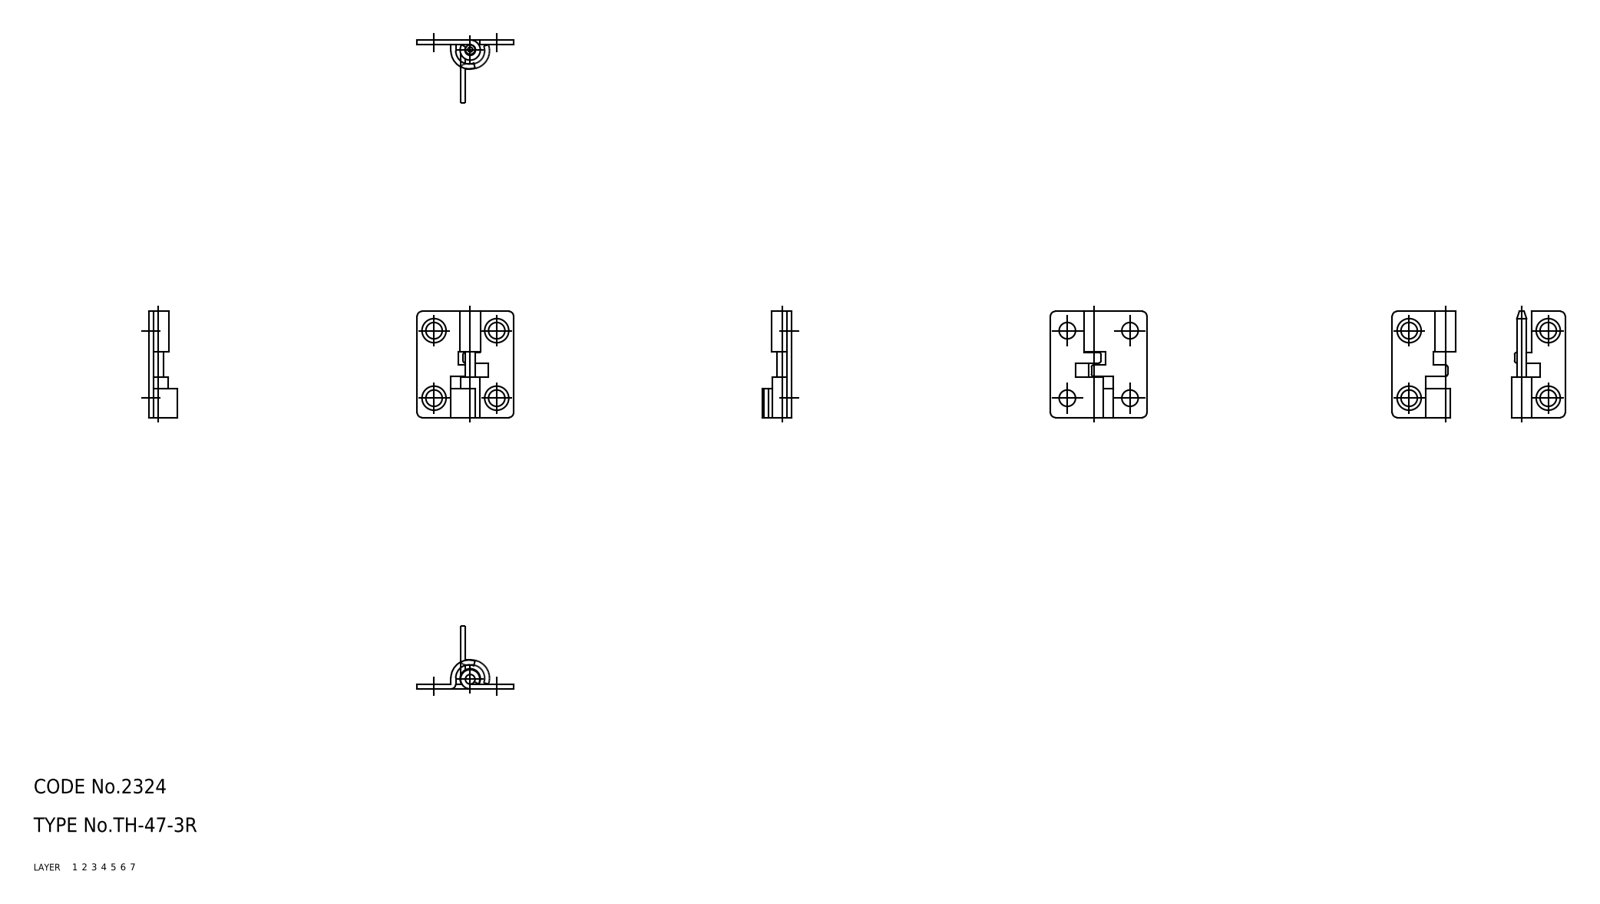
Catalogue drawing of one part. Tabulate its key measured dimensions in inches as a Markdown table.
| quantity | value |
| --- | --- |
| part name | 67112309; 67112322; 67112335 |
| STEP written by | CADfix (AUTOMOTIVE_DESIGN) |
| units | inches |
| bodies | 3 solids, 65 faces (0 planar, 0 cylindrical, 65 other) |
| overall size | 0.866 × 0.787 × 0.236 |
| volume | 0.035 in³ |
| surface area | 2.175 in² |
